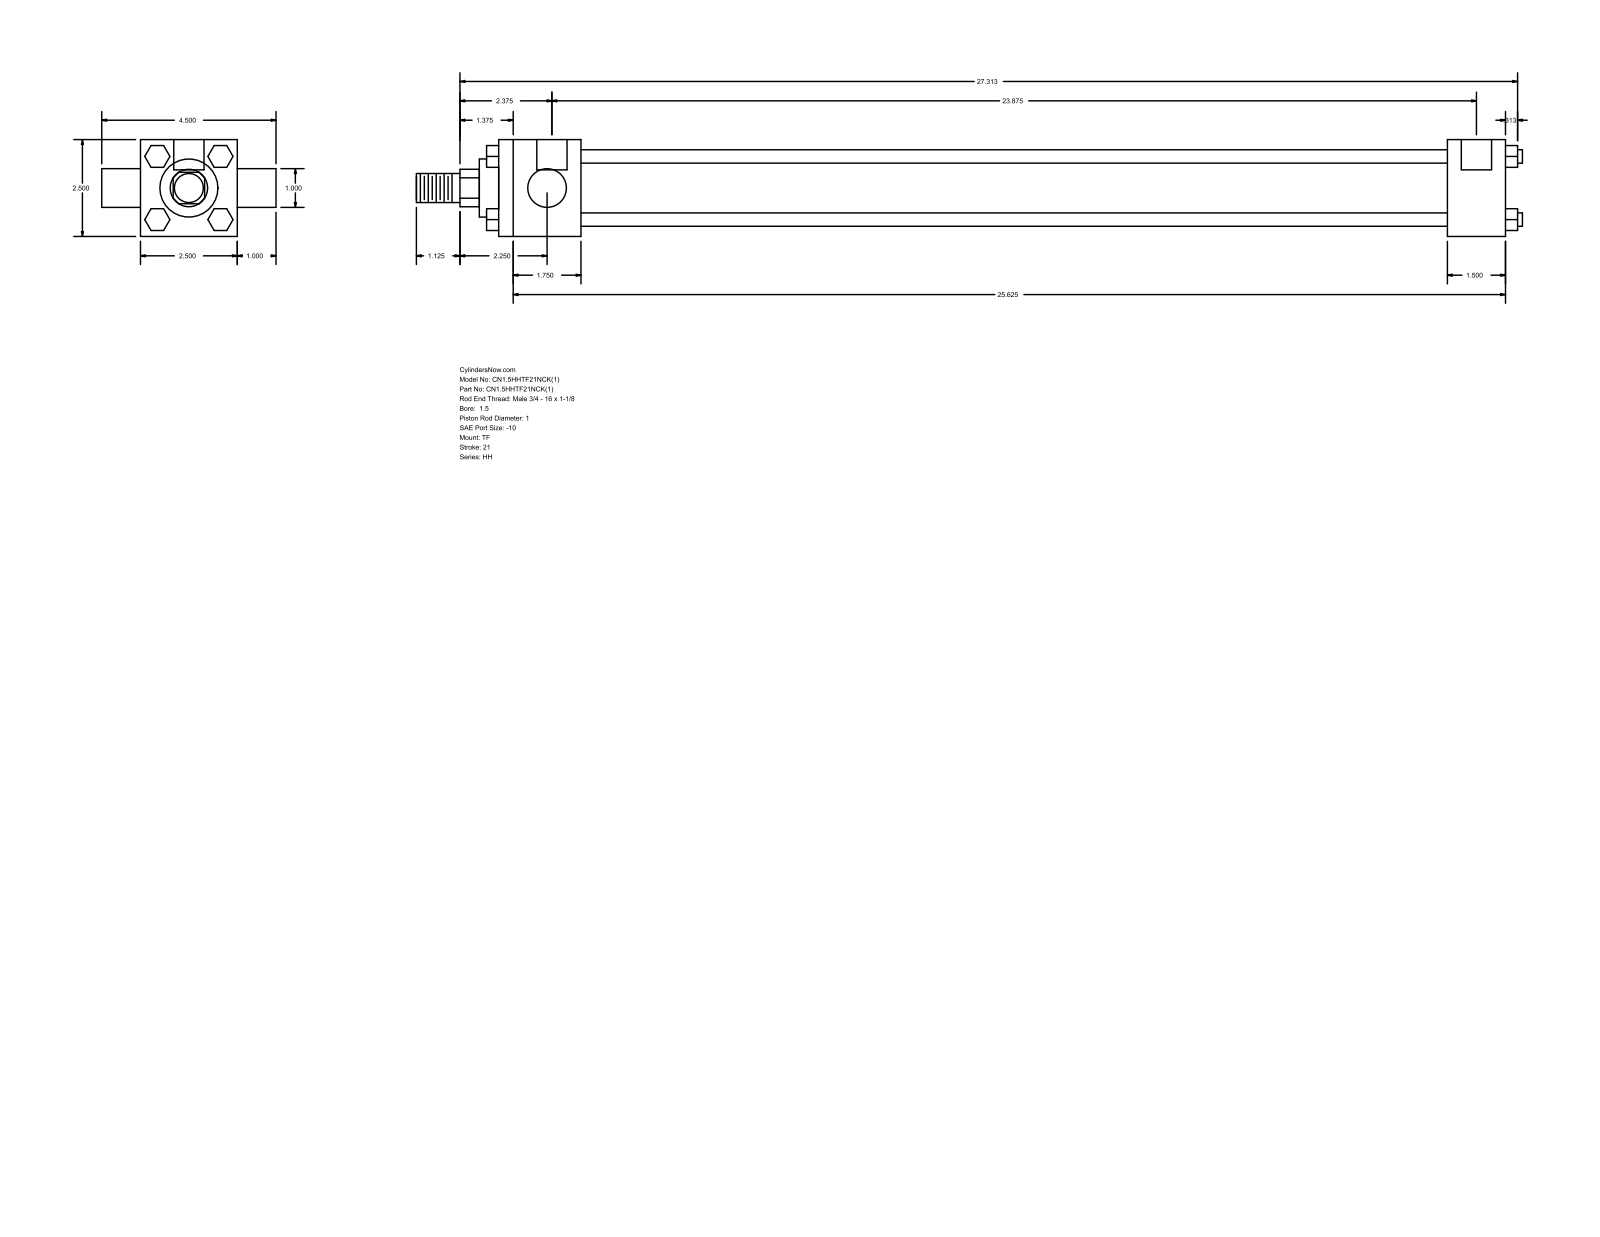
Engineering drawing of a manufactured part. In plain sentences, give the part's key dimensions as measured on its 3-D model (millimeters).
The part is named "HH_TF__0150_1". Its 3-D file was written by "GSSL Pune (CONFIG_CONTROL_DESIGN)". It is 0 solids with 120 faces: 92 planar, 28 cylindrical and 0 other. Overall it measures 725.49 by 114.3 by 63.5 millimeters. Round holes: 3 of diameter 5.56, 2 of diameter 19.84. Round bosses or shafts: 4 of diameter 8.76, 2 of diameter 25.4, 1 of diameter 44.45, 1 of diameter 38.1, 1 of diameter 19.05. Partial cylindrical surfaces (rounded edges, fillets, slot ends): 1 of radius 12.29. The main face-to-face distances are 63.5, 38.1, 606.42, 568.32, 53.98, 622.3, 660.4, 25.4, 20.7, 14.29. The hole center spacings are 1.59, 608.01, 606.42, 609.6.
